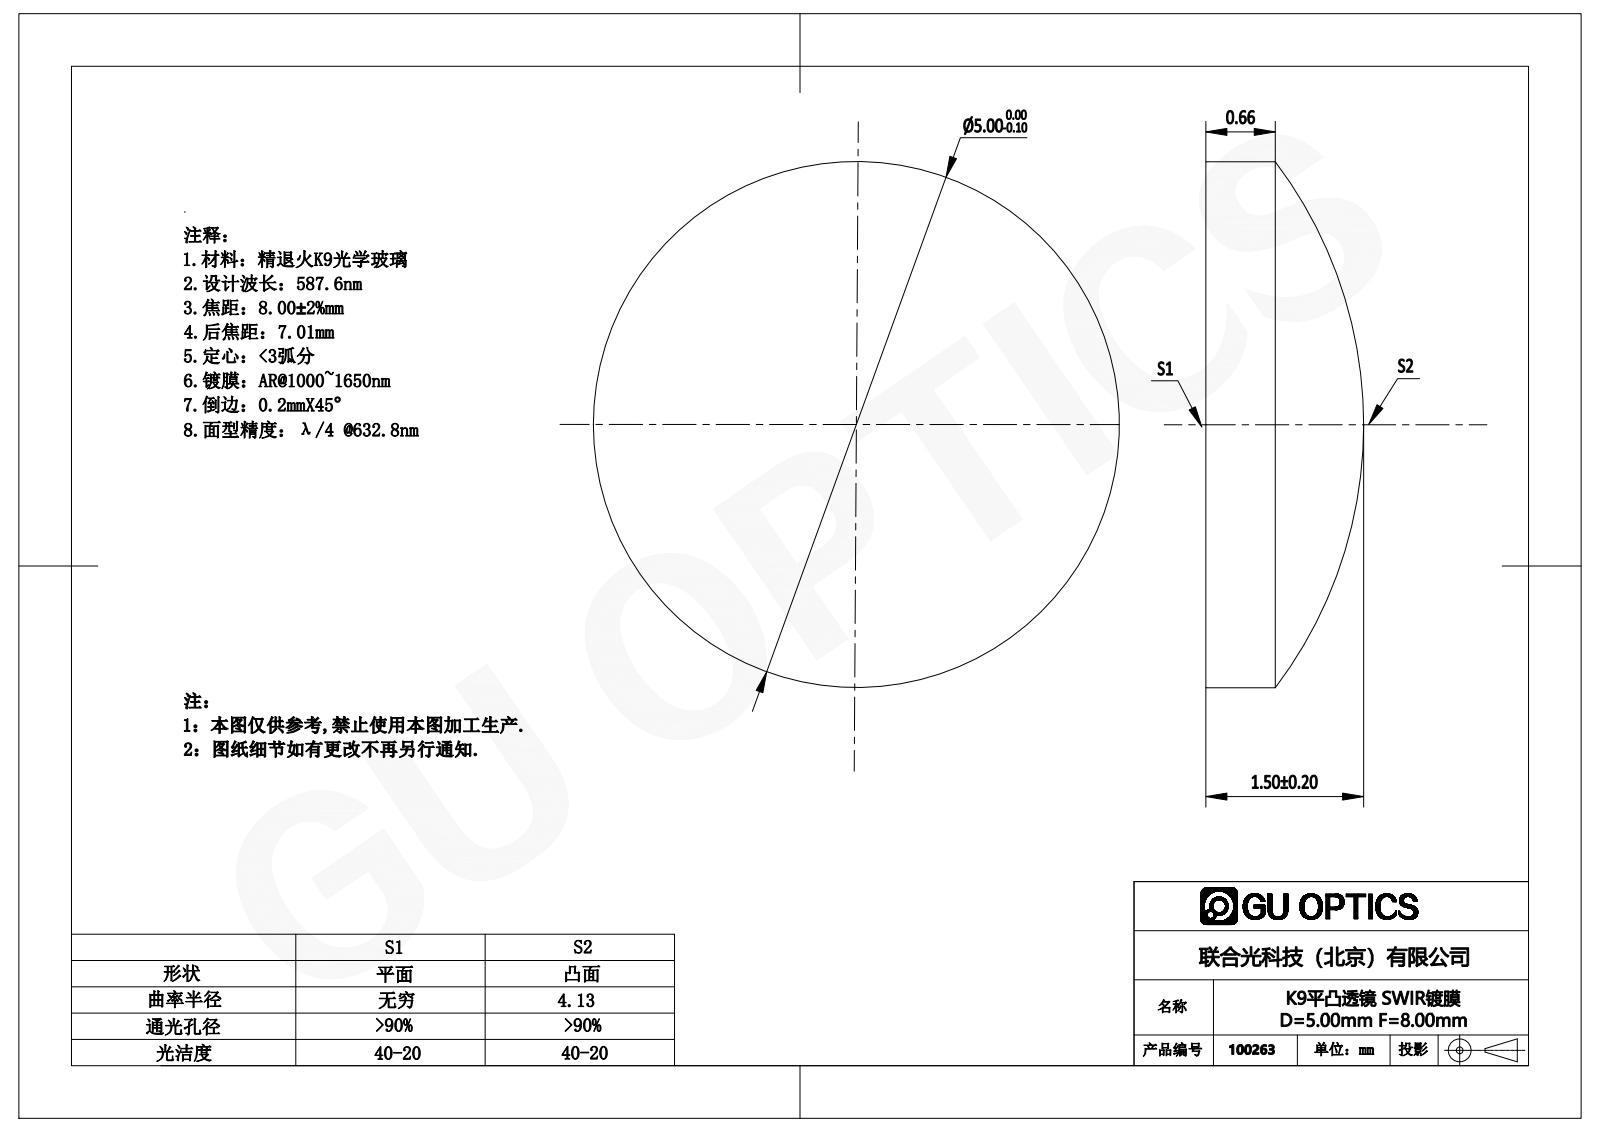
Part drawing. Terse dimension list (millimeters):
name: 100091
written by: SolidWorks 2016 (AUTOMOTIVE_DESIGN)
unit: mm
bodies: 1 solid, 5 faces (1 planar, 2 cylindrical, 2 other)
size: 5 × 5 × 1.5
volume: 22 mm³; area: 52 mm²
bosses: 1× ⌀5
